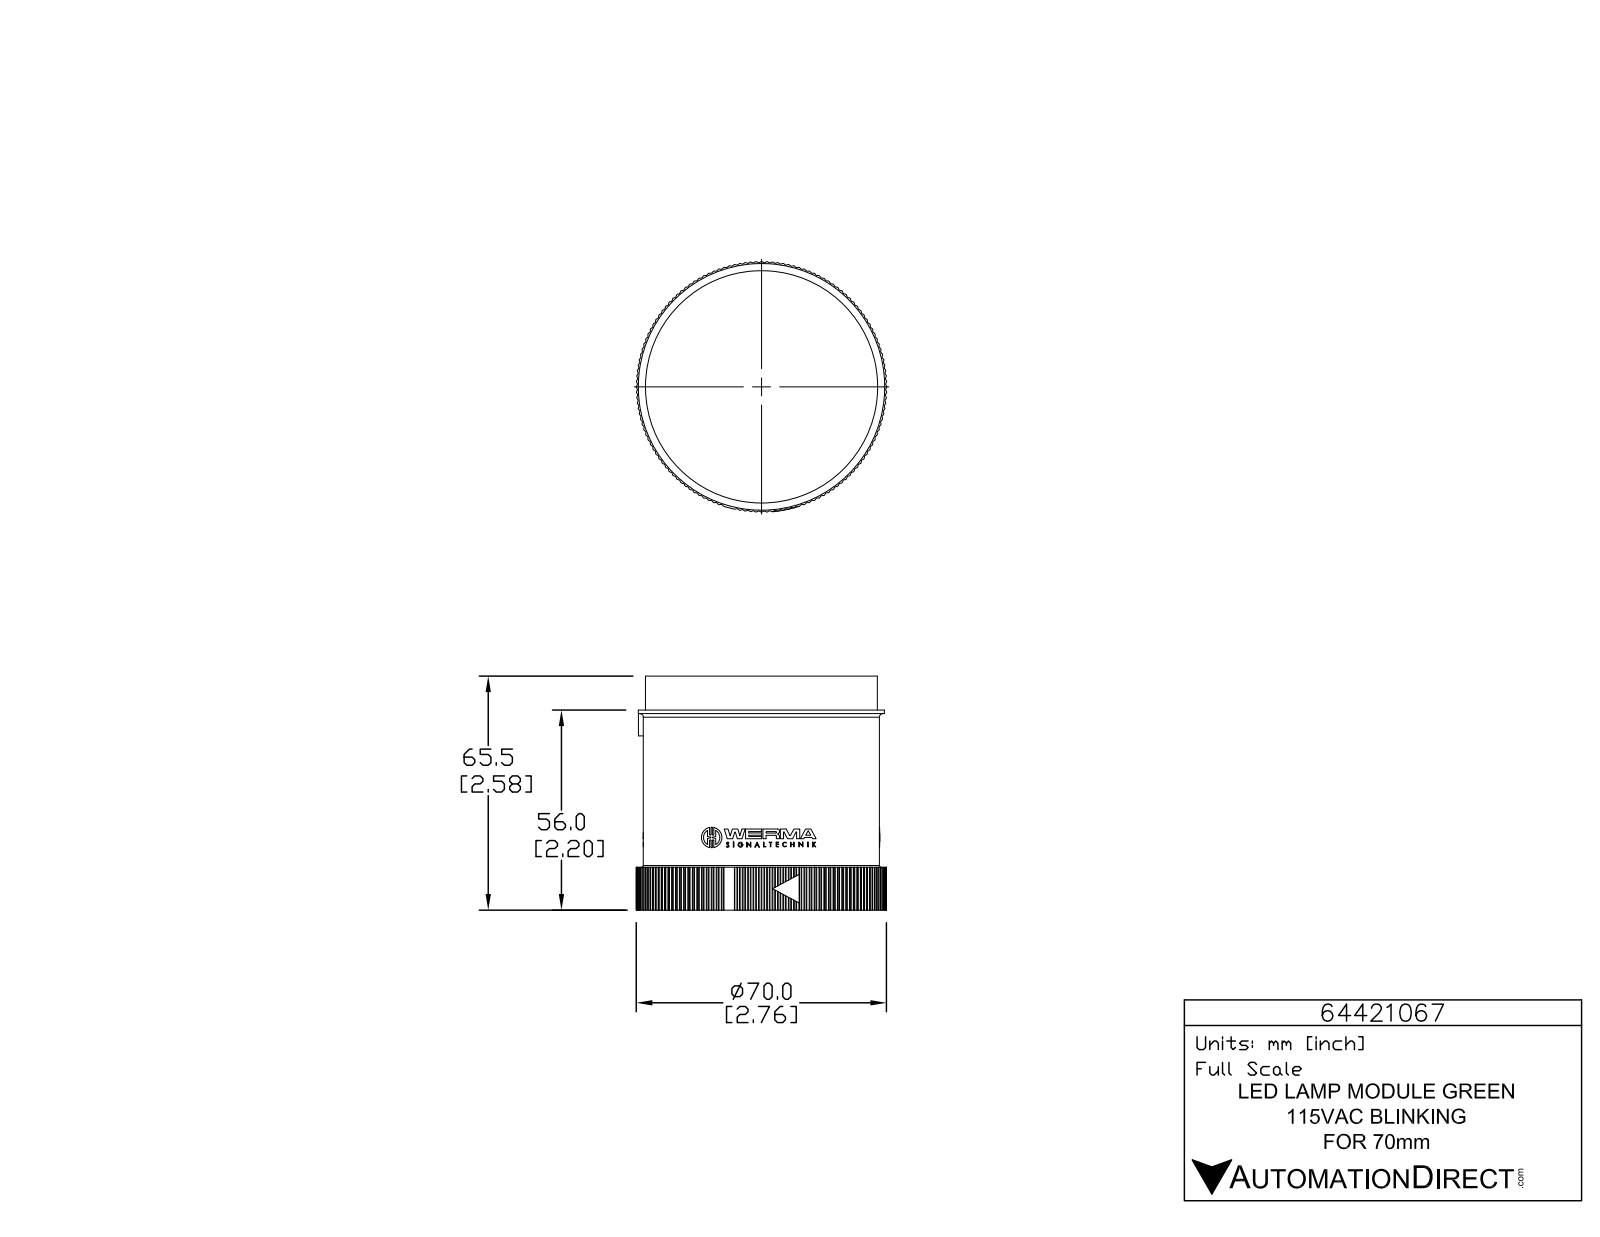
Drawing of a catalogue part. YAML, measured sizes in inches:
part_name: "64421067"
step_written_by: "SolidWorks 2015 (AUTOMOTIVE_DESIGN)"
units: inches
bodies: {solids: 1, faces: 1400, planar: 832, cylindrical: 563, other: 5}
overall_size: [2.762, 2.762, 2.579]
volume: 12.02
surface_area: 37.48
round_holes:
  - {diameter: 0.039, count: 3}
  - {diameter: 2.575, count: 1}
round_bosses_or_shafts:
  - {diameter: 0.226, count: 3}
  - {diameter: 0.056, count: 3}
  - {diameter: 2.717, count: 1}
  - {diameter: 2.606, count: 1}
  - {diameter: 2.559, count: 1}
partial_cylinders:
  - {radius: 0.008, count: 285}
  - {radius: 0.008, count: 6}
  - {radius: 0.008, count: 6}
  - {radius: 0.008, count: 6}
  - {radius: 0.131, count: 6}
  - {radius: 0.004, count: 3}
  - {radius: 0.005, count: 3}
  - {radius: 0.008, count: 3}
face_to_face_distances: [2.201, 2.451, 0.378, 2.579, 2.205, 1.827, 0.374, 2.452, 0.472, 0.094]
